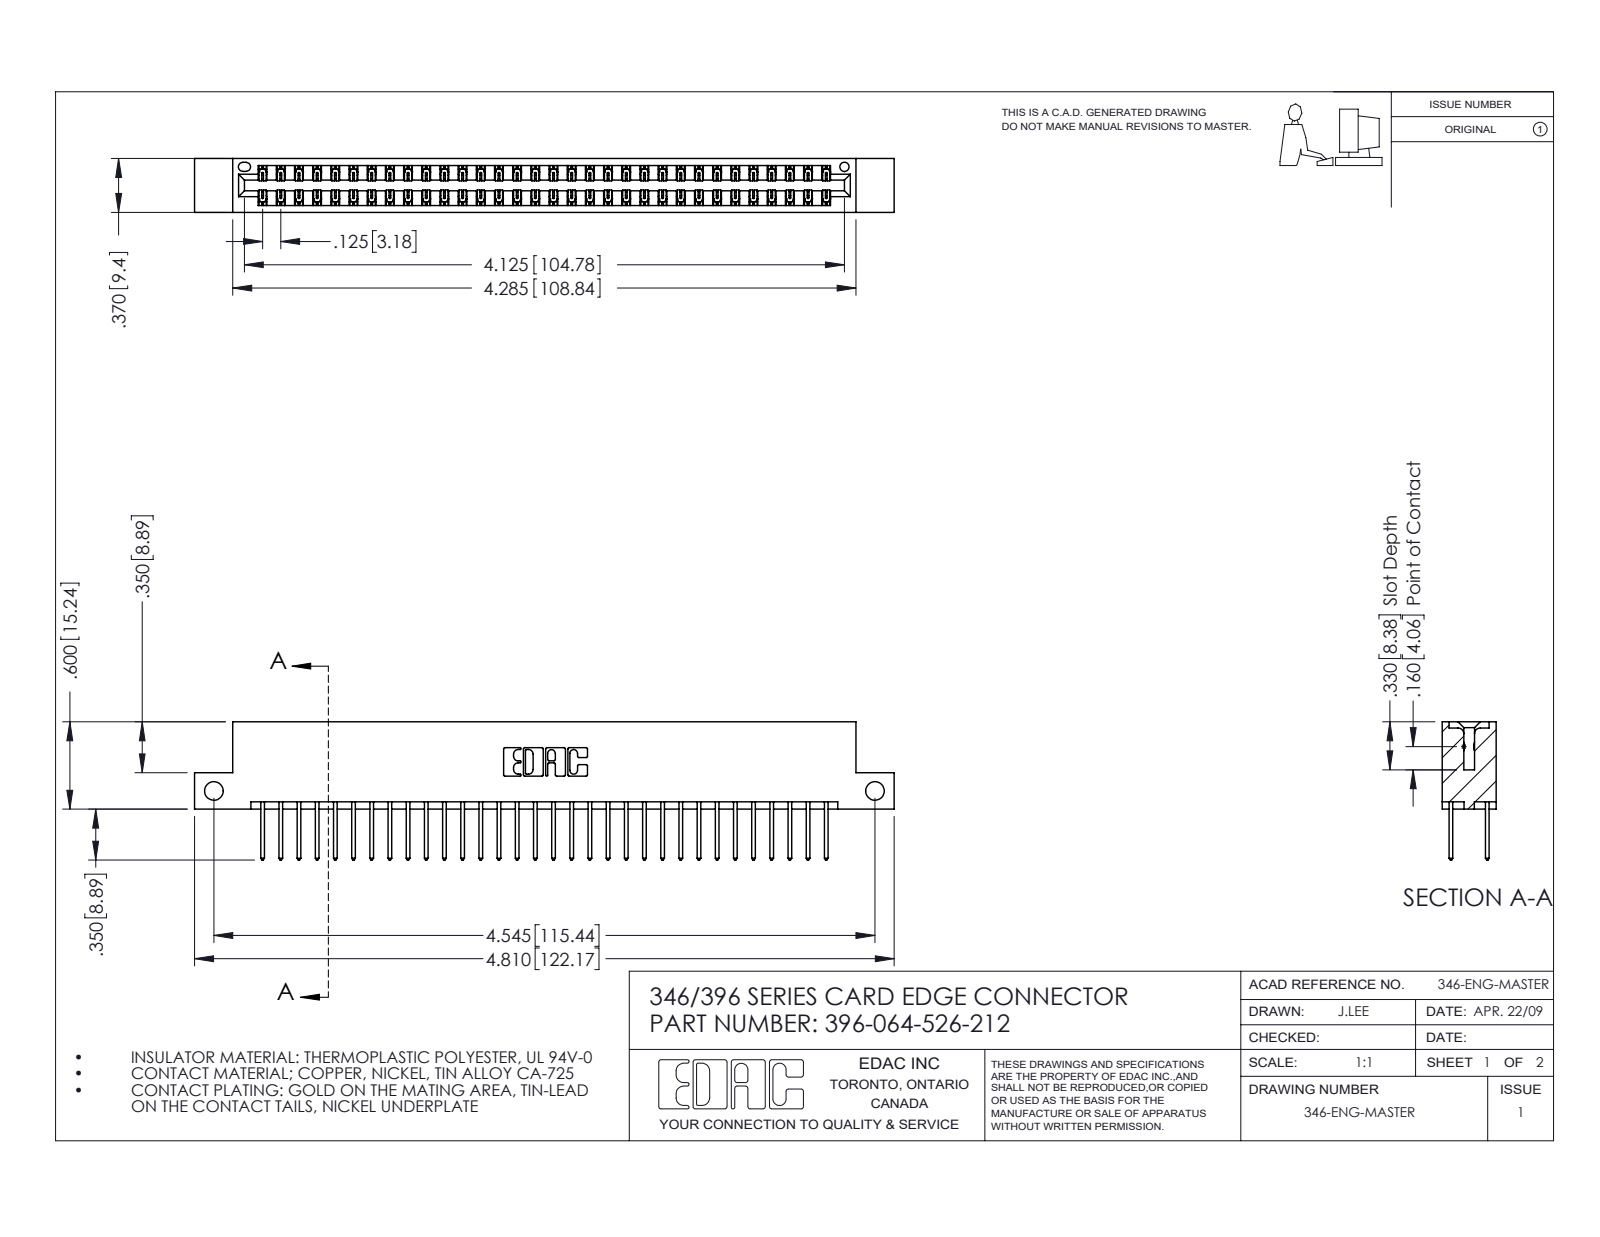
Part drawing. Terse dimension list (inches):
name: 346 Part_Flush Mounting Lugs - Side Mount; 396-064-526-212; 345-292-001_345-293-126
written by: SolidWorks 2016 (CONFIG_CONTROL_DESIGN)
unit: in
bodies: 65 solids, 3450 faces (2316 planar, 1134 cylindrical, 0 other)
size: 4.81 × 0.95 × 0.37
volume: 0.723 in³; area: 25.53 in²
holes: 2× ⌀0.128, 1× ⌀0.064
rounds: 96× R0.006, 64× R0.01, 22× R0.01, 6× R0.007, 6× R0.031, 3× R0.026, 2× R0.014, 2× R0.022
face distances: 0.048, 0.322, 0.25, 0.37, 0.072, 0.298, 0.025, 0.275, 0.148, 0.222
hole spacings: 4.545
